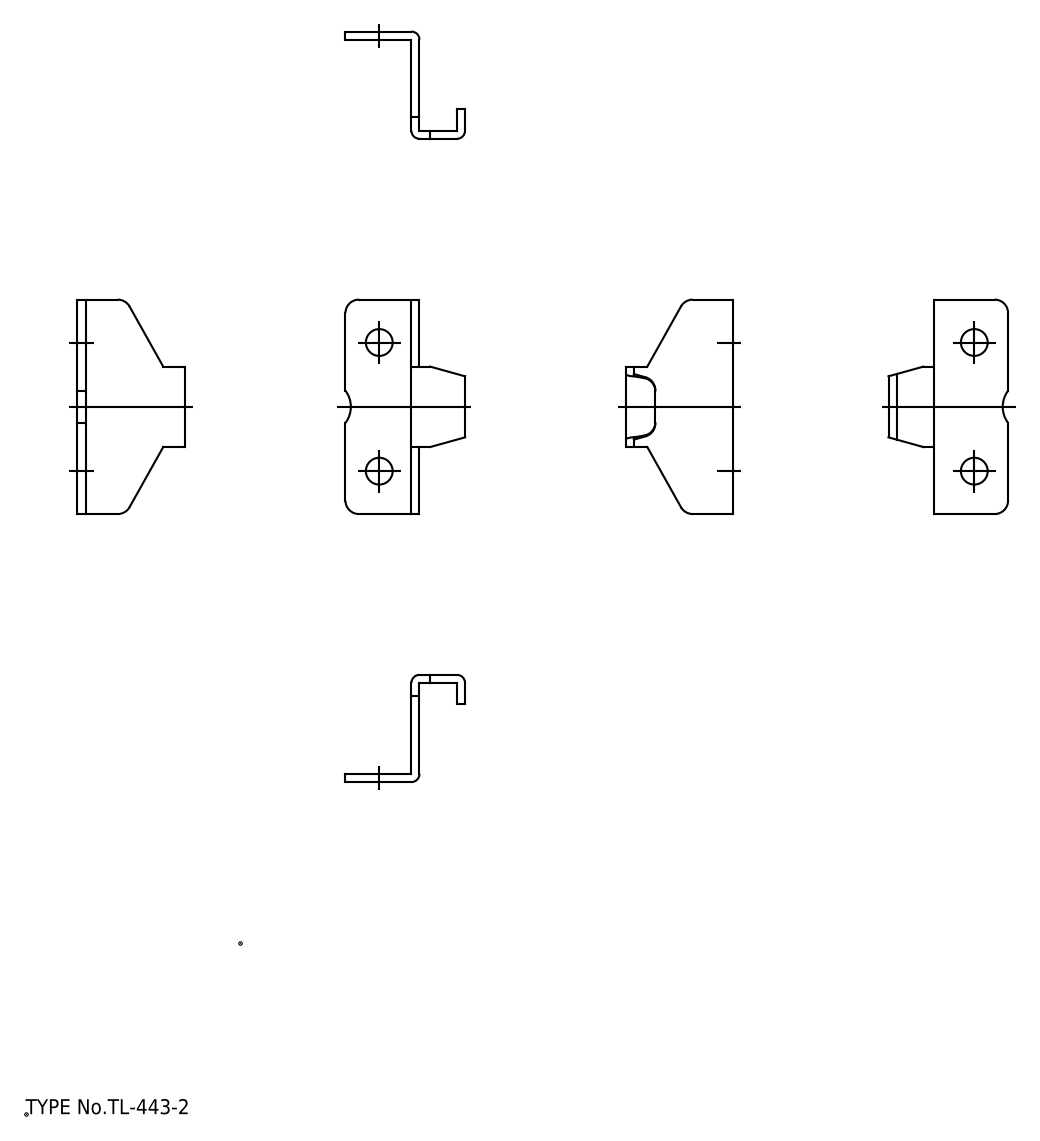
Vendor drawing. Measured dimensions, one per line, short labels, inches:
written by: spGate 19.8.4 (****-****-****-****) (AUTOMOTIVE_DESIGN)
unit: in
bodies: 1 solid, 35 faces (19 planar, 12 cylindrical, 4 other)
size: 1.575 × 0.878 × 0.787
volume: 0.109 in³; area: 4.121 in²
holes: 2× ⌀0.197
rounds: 4× R0.098, 3× R0.059, 1× R0.197
face distances: 0.059, 0.728, 0.787, 0.669, 0.335, 0.484, 0.543, 0.819, 0.276, 0.878
hole spacings: 0.945
